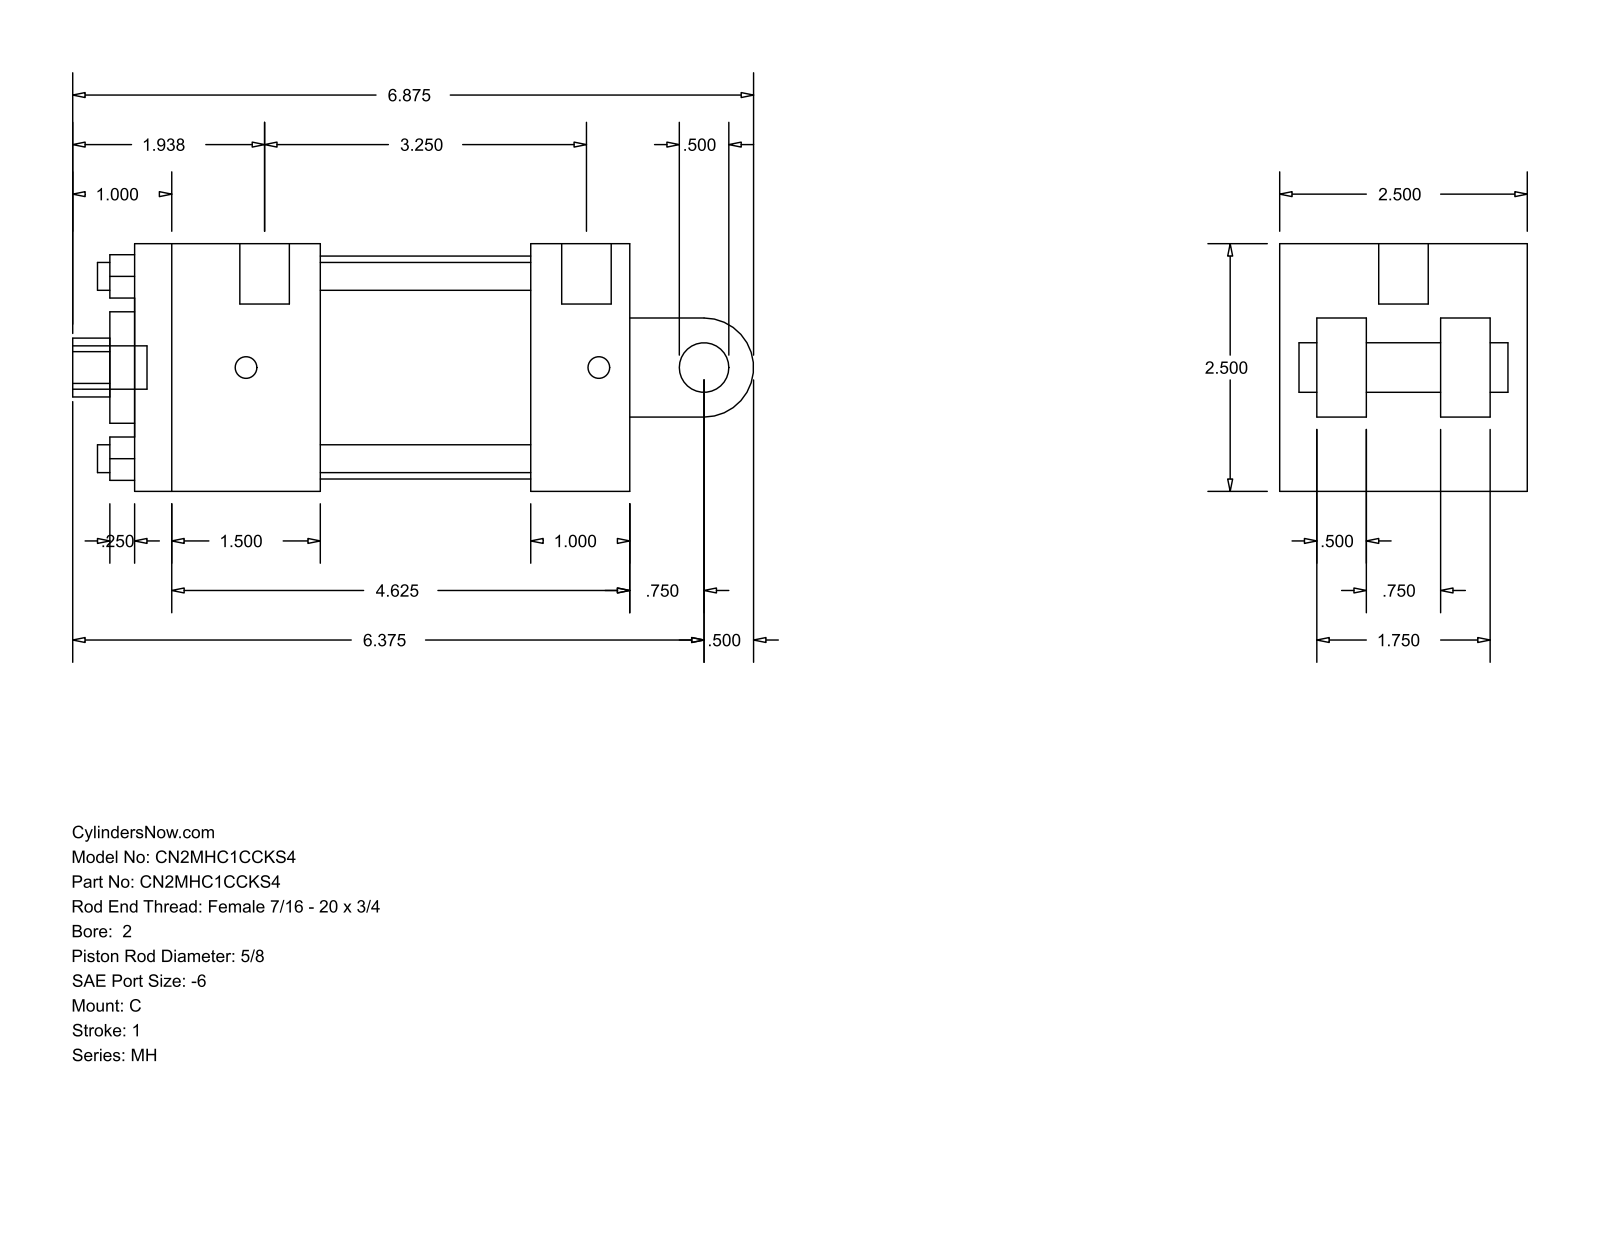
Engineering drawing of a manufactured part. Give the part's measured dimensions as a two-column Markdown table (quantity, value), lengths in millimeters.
| quantity | value |
| --- | --- |
| part name | MH_C__0200_0.625 |
| STEP written by | GSSL Pune (CONFIG_CONTROL_DESIGN) |
| units | millimeters |
| bodies | 0 solids, 99 faces (70 planar, 29 cylindrical, 0 other) |
| overall size | 174.62 × 63.5 × 63.5 |
| round holes (diameter × count) | 7.14 × 4, 5.56 × 2, 12.7 × 1, 15.88 × 1, 28.57 × 1, 57.15 × 1 |
| round bosses / shafts (diameter × count) | 12.7 × 2, 5.56 × 2, 11.11 × 1 |
| partial cylindrical surfaces (radius × count) | 7.54 × 1, 12.7 × 1 |
| main face-to-face distances | 63.5, 127, 53.97, 12.7, 9.52, 47.62, 101.59, 79.38, 25.41, 19.05 |
| hole center spacings | 33.05, 46.74, 66.1, 3.18 |
